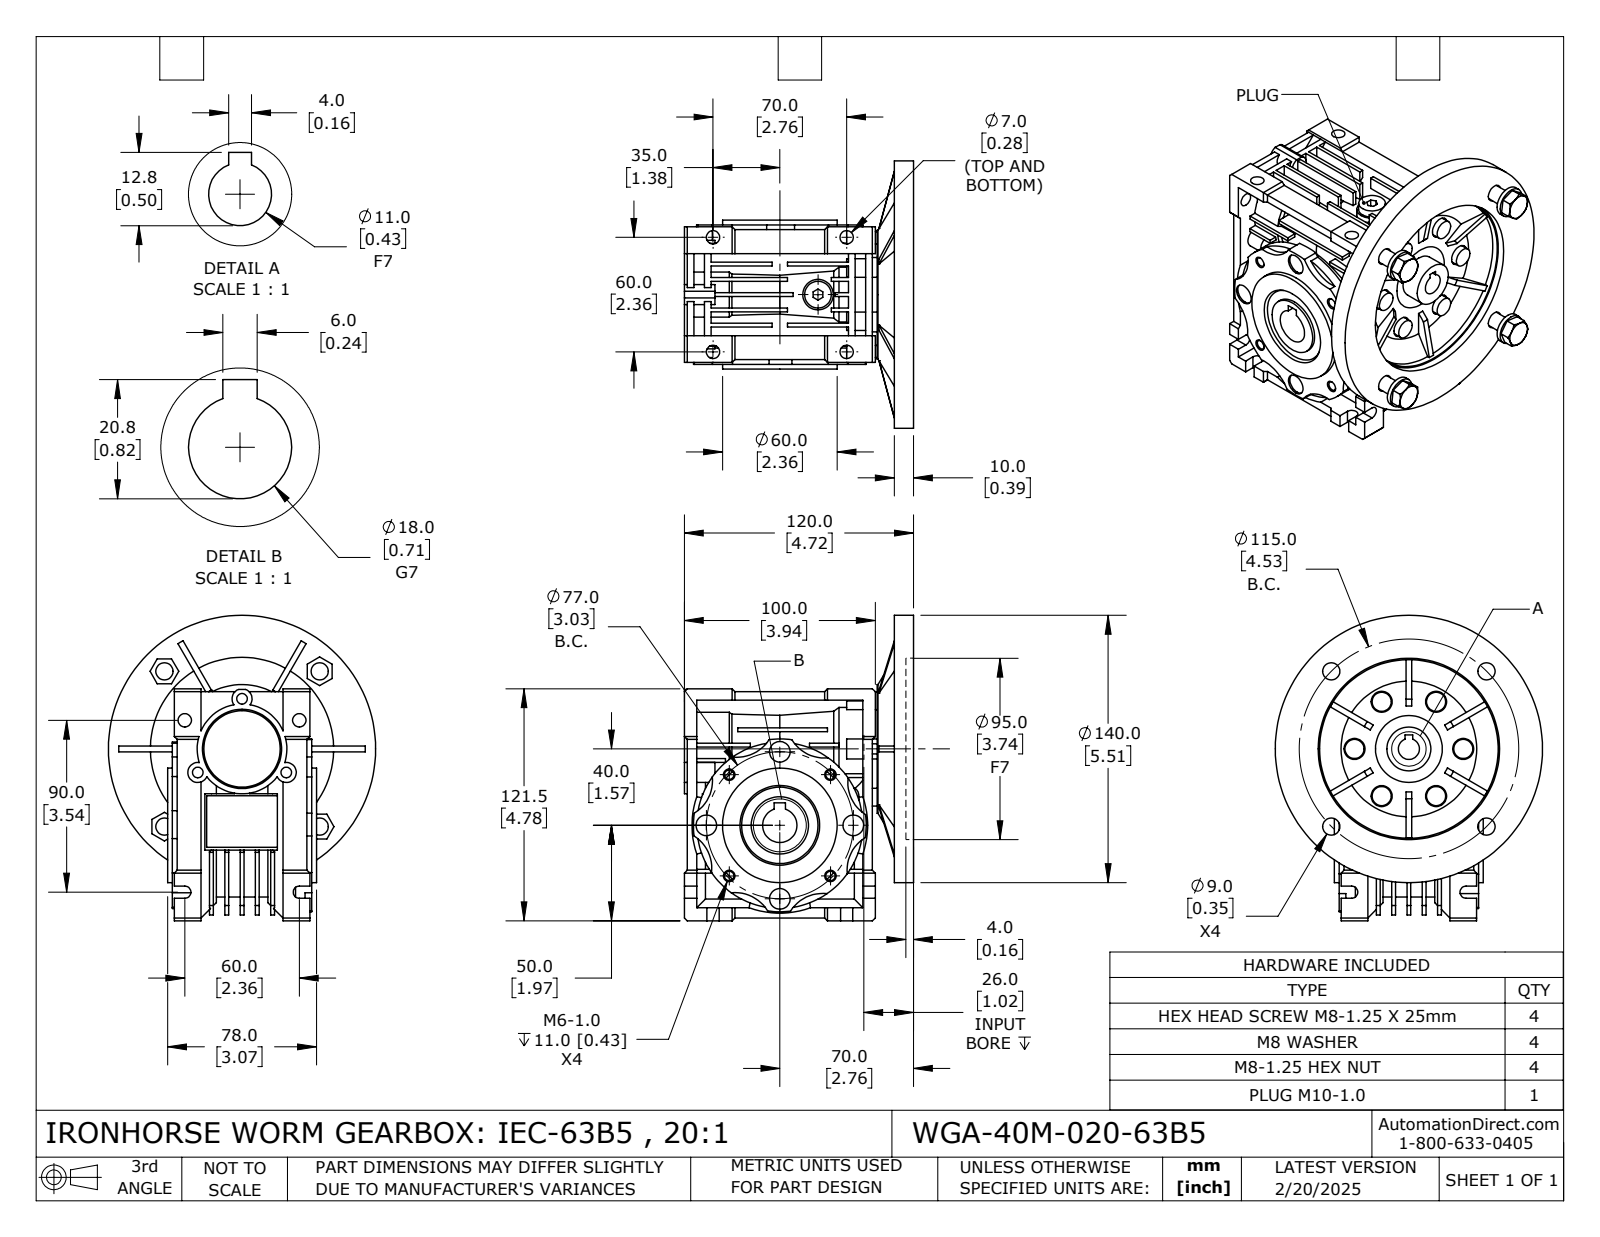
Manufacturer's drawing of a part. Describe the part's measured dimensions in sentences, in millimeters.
The part is named "WGA-40M-020-63B5". Its 3-D file was written by "SolidWorks 2024 (CONFIG_CONTROL_DESIGN)". It is 18 solids with 1083 faces: 592 planar, 298 cylindrical and 193 other. Overall it measures 160 by 140 by 137.98 millimeters. Its volume is 749 957 cubic millimeters and its surface area 190 617 square millimeters. Round holes: 7 of diameter 11, 6 of diameter 7, 5 of diameter 9, 4 of diameter 4.92, 4 of diameter 6.8, 4 of diameter 8, 4 of diameter 9.12, 4 of diameter 10.8, 3 of diameter 5.55, 1 of diameter 11.5, 1 of diameter 18, 1 of diameter 23. Round bosses or shafts: 6 of diameter 10, 5 of diameter 16, 1 of diameter 140, 1 of diameter 75, 1 of diameter 67.5, 1 of diameter 60, 1 of diameter 54, 1 of diameter 47. Partial cylindrical surfaces (rounded edges, fillets, slot ends): 8 of radius 20, 6 of radius 3.2, 6 of radius 5.22, 3 of radius 5.25, 1 of radius 43.5, 1 of radius 43.59, 1 of radius 45.25, 1 of radius 46. The main face-to-face distances are 10, 8, 6, 2, 5, 1.5, 16, 24, 14, 2.5. The hole center spacings are 28.5, 29.1, 70.22, 49.36, 30.87, 33.54, 37.5, 38.5.
